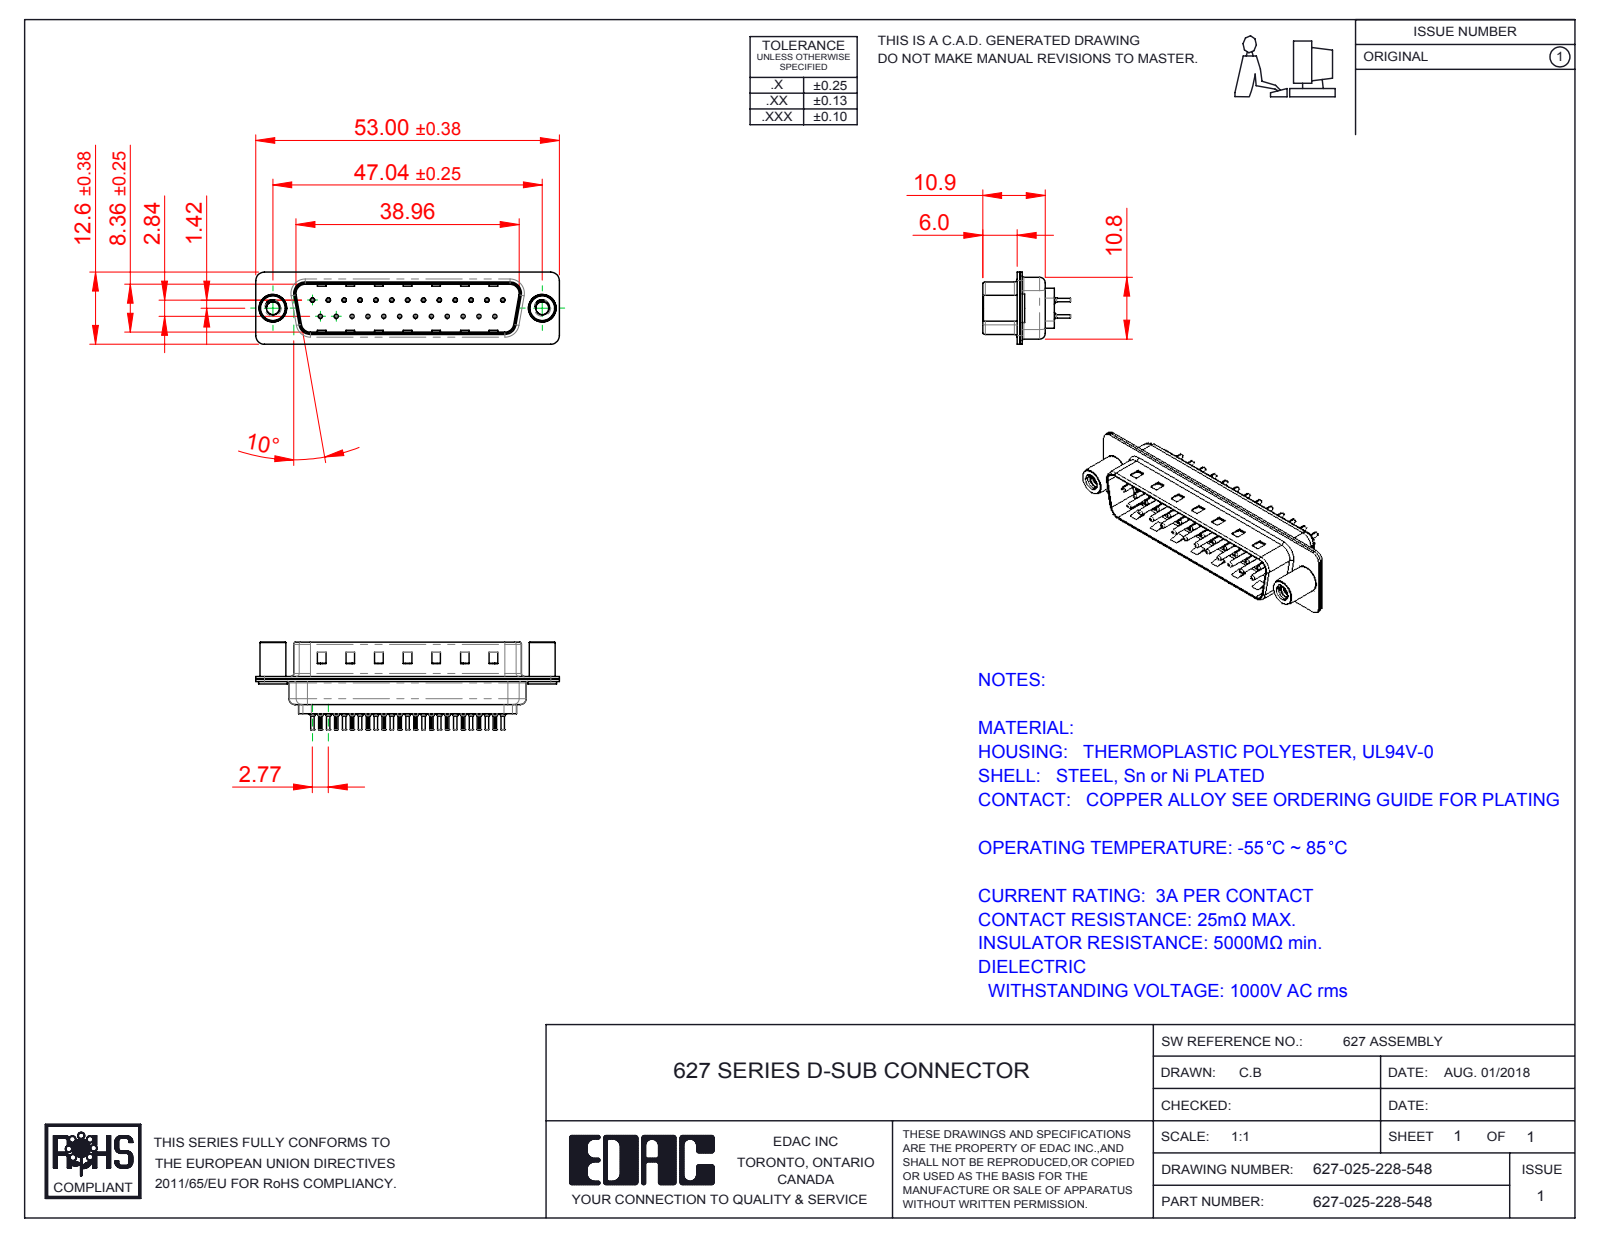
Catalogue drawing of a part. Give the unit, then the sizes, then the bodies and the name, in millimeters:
Units: millimetres
Overall size (bounding box): 53 × 15.3 × 12.6
Round holes (diameter × count): ⌀0.2 ×25, ⌀0.35 ×25, ⌀1.1 ×25, ⌀1.6 ×25, ⌀2.26 ×2, ⌀4 ×2, ⌀4.8 ×2
Round bosses / shafts (diameter × count): ⌀2 ×25, ⌀1.5 ×25, ⌀0.75 ×25, ⌀0.6 ×25, ⌀5 ×2, ⌀4.9 ×2, ⌀4.5 ×2
Partial cylindrical surfaces — rounded edges, fillets, slot ends (radius × count): R0.1 ×50, R1.5 ×16, R2 ×12, R0.5 ×8, R1.6 ×8, R0.25 ×4, R0.6 ×4, R0.65 ×4
Main face-to-face distances: 0.4, 0.45, 0.82, 9.58, 0.9, 8.76, 1.5, 1.4, 6.5, 6.05
Hole centre spacings: 3.16, 8.31, 2.77, 5.54, 11.08, 16.62, 5.03, 5.04
Volume: 2 734 mm³ · Surface area: 7 860 mm²
Bodies: 30 solids, 2860 faces (773 planar, 1090 cylindrical, 997 other)
Part name (STEP PRODUCT): 627 Shell Front_25 Contacts; 627 Shell Rear_25 Contacts; 627-025-228-548; 627 4-40 Threaded Standoff (+3 more)
STEP written by: SolidWorks 2016 (CONFIG_CONTROL_DESIGN)
